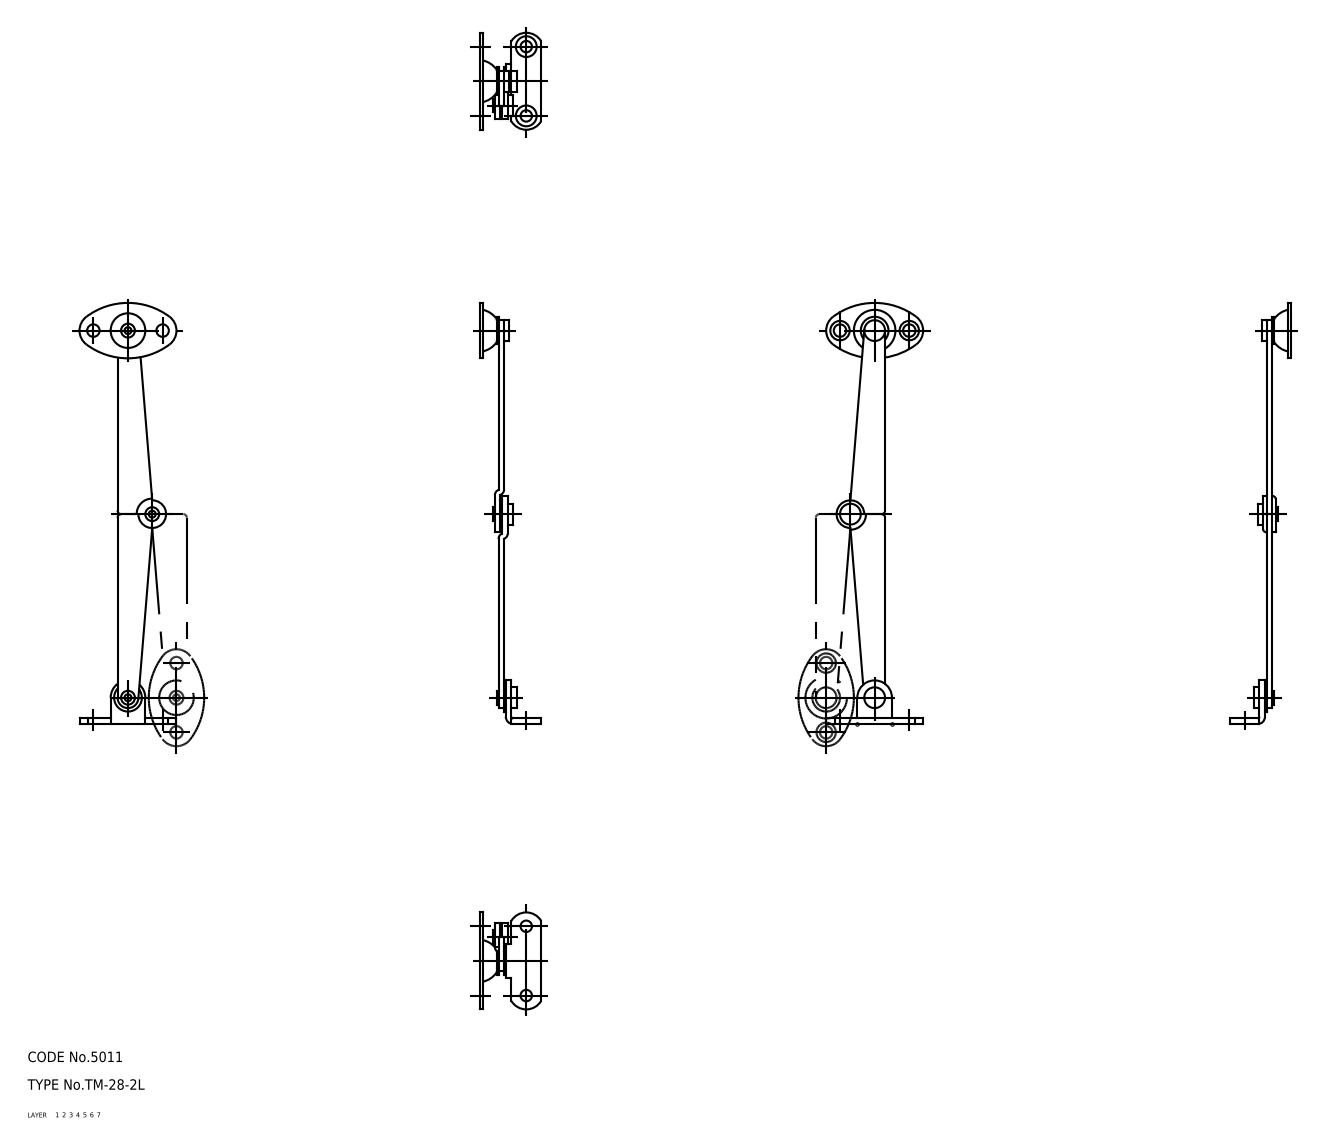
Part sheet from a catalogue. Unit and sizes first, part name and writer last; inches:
Units: inches
Overall size (bounding box): 4.787 × 1.102 × 0.701
Volume: 0.167 in³ · Surface area: 7.595 in²
Bodies: 10 solids, 125 faces (0 planar, 0 cylindrical, 125 other)
Part name (STEP PRODUCT): washer; rivet_1; arm; rivet_2 (+3 more)
STEP written by: CADfix (AUTOMOTIVE_DESIGN)
